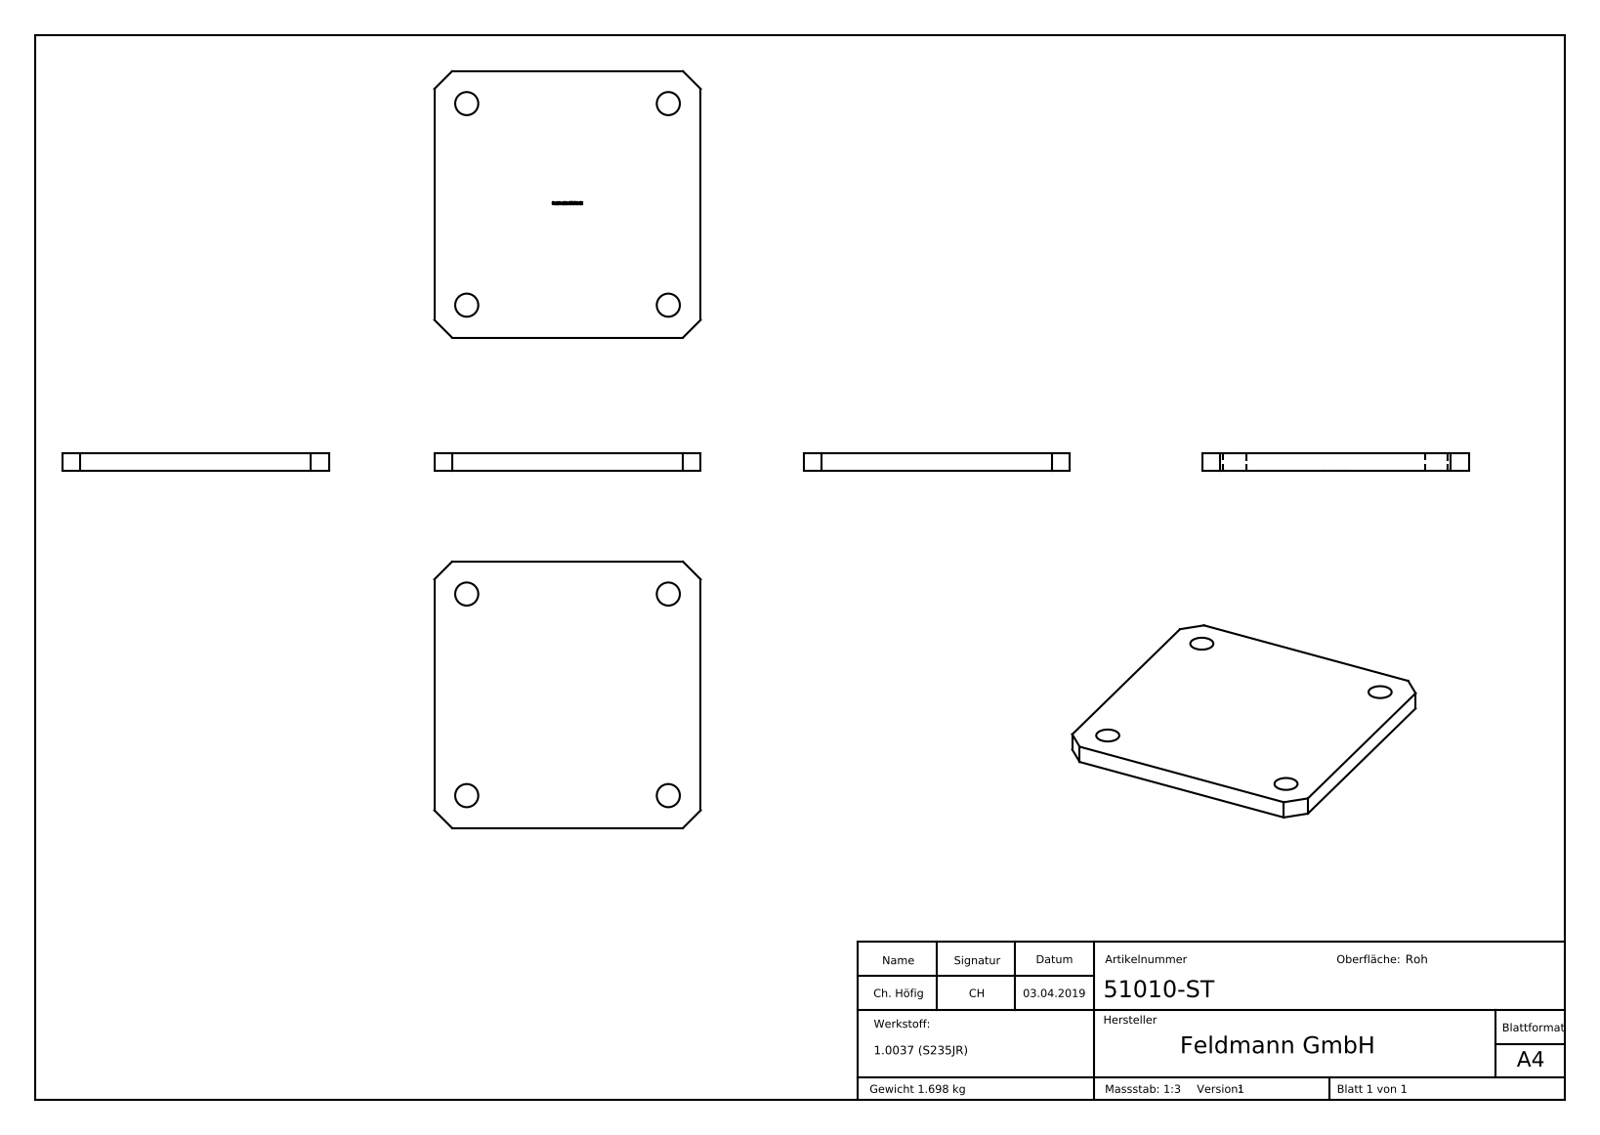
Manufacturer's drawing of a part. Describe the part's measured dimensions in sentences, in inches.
The part is named "51010-ST". Its 3-D file was written by "SolidWorks 2015 (CONFIG_CONTROL_DESIGN)". It is 1 solid with 214 faces: 117 planar, 8 cylindrical and 89 other. Overall it measures 5.906 by 5.906 by 0.394 inches. Its volume is 13.28 cubic inches and its surface area 78.97 square inches. Round holes: 4 of diameter 0.512. The main face-to-face distances are 0.394, 5.906, 7.794, 0.39, 2.953, 0.343, 0.423, 0.08, 0.117, 0.08. The hole center spacings are 4.469, 6.319.
